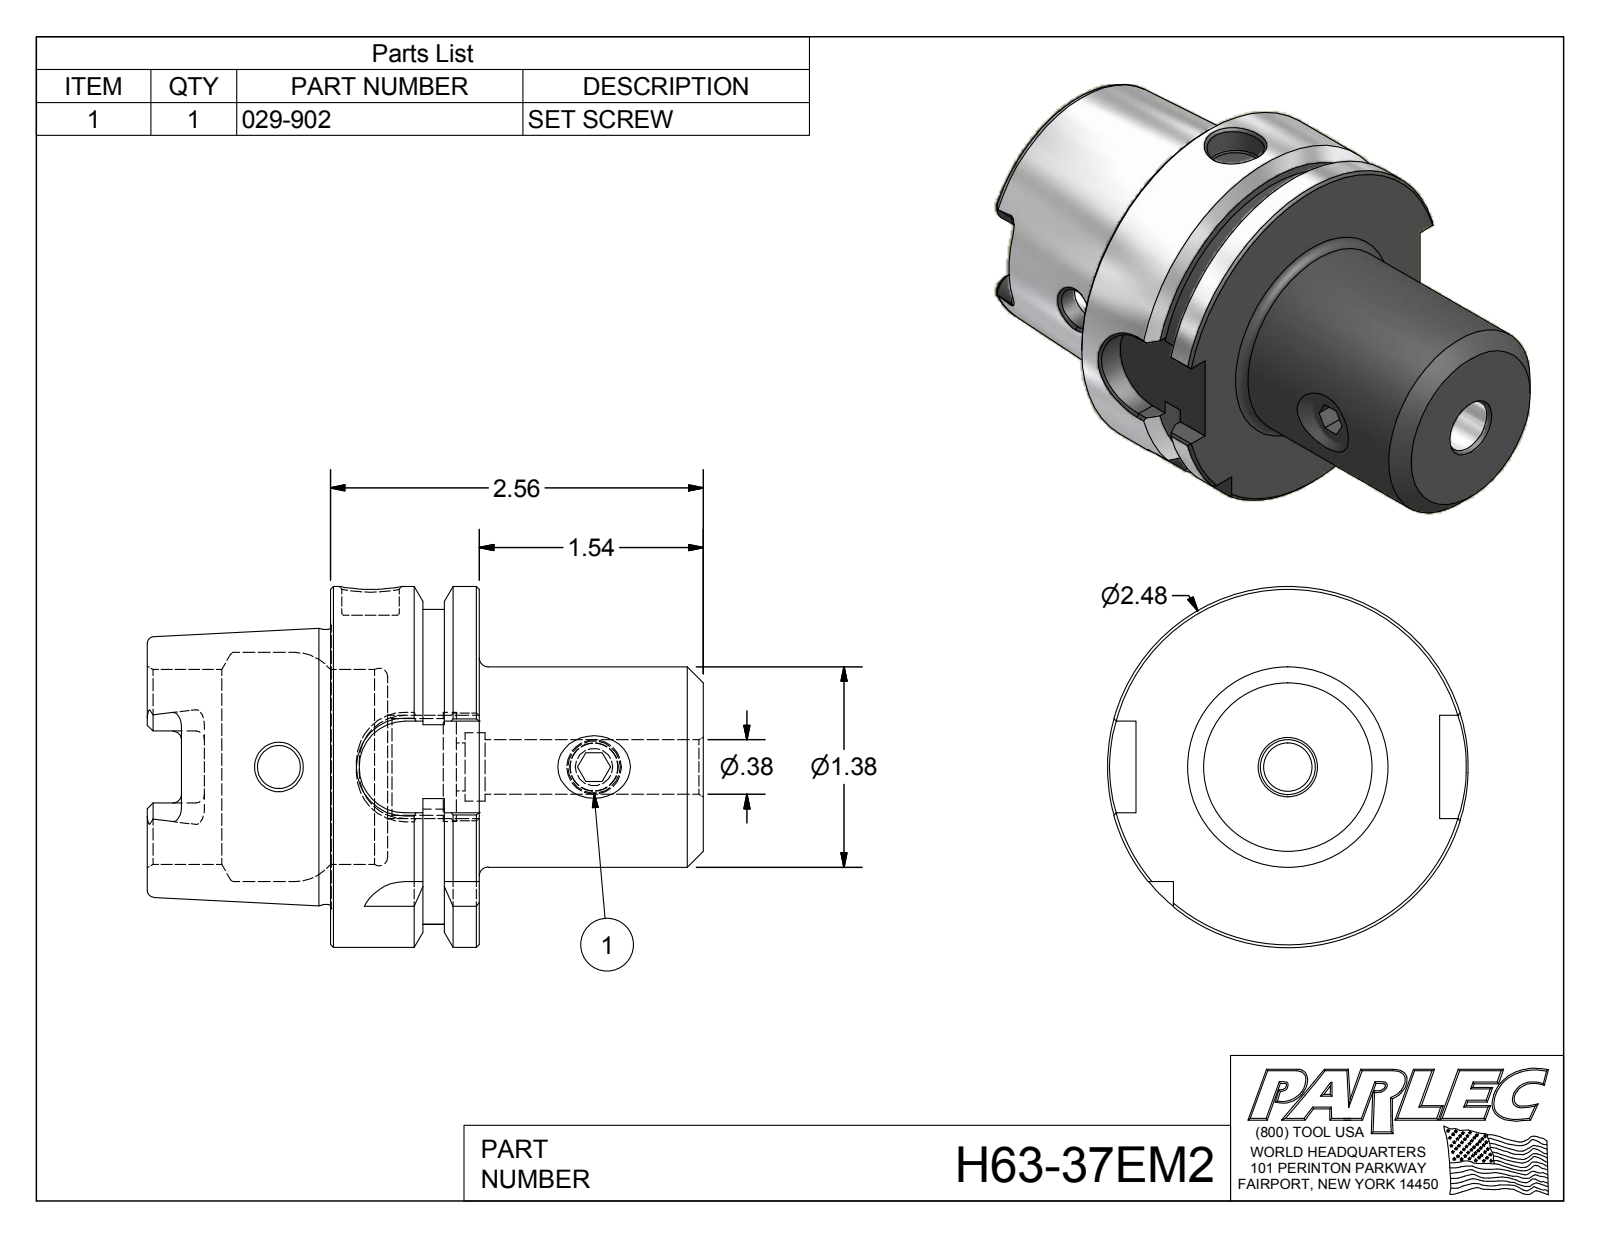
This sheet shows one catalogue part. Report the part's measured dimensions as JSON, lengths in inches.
{"part_name": "H63-37EM2; 029-902", "step_written_by": "Autodesk Inventor 2012 (AUTOMOTIVE_DESIGN)", "units": "inches", "bodies": {"solids": 2, "faces": 149, "planar": 62, "cylindrical": 37, "other": 50}, "overall_size": [3.822, 2.48, 2.48], "volume_in3": 7.015, "surface_area_in2": 44.15, "round_holes": [[0.295, 1], [0.33, 1], [0.331, 1], [0.375, 1], [0.394, 1], [0.47, 1], [0.666, 1], [0.749, 1], [1.339, 1], [1.575, 1]], "round_bosses_or_shafts": [[2.48, 1], [1.891, 1], [1.378, 1], [0.375, 1]], "partial_cylinders_radius": [[0.059, 6], [0.113, 4], [0.315, 4], [1.083, 1]], "face_to_face_distances": [1.024, 0.241, 0.389, 2.562, 1.538, 0.394, 0.63, 2.168, 1.26, 1.654], "hole_center_spacings": [2.166]}
